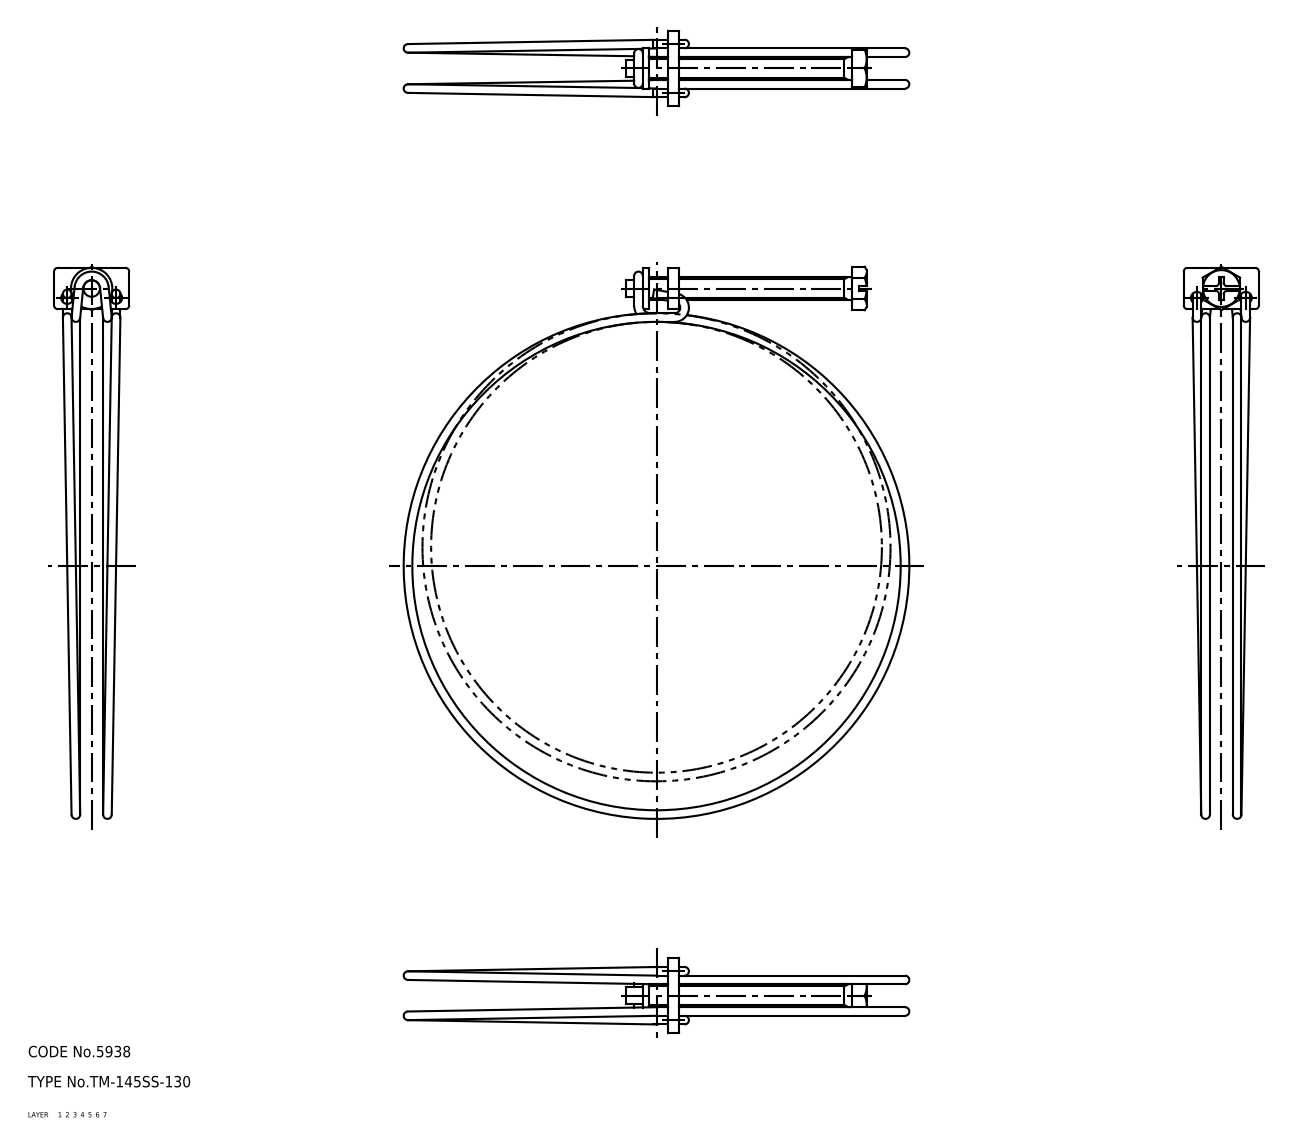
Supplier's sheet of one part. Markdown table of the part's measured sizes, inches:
| quantity | value |
| --- | --- |
| part name | screw; holder; band; TM_145SS_130 |
| STEP written by | SolidWorks 2015 (AUTOMOTIVE_DESIGN) |
| units | inches |
| bodies | 3 solids, 95 faces (31 planar, 36 cylindrical, 28 other) |
| overall size | 5.793 × 5.3 × 0.787 |
| volume | 0.386 in³ |
| surface area | 13.66 in² |
| round holes (diameter × count) | 0.126 × 2, 0.236 × 1 |
| round bosses / shafts (diameter × count) | 0.091 × 8, 0.433 × 1, 0.173 × 1 |
| partial cylindrical surfaces (radius × count) | 0.039 × 8 |
| main face-to-face distances | 0.118, 0.197, 0.26, 0.378, 0.433, 0.063, 0.315, 0.394, 2.346, 2.283 |
| hole center spacings | 0.274, 0.512 |
